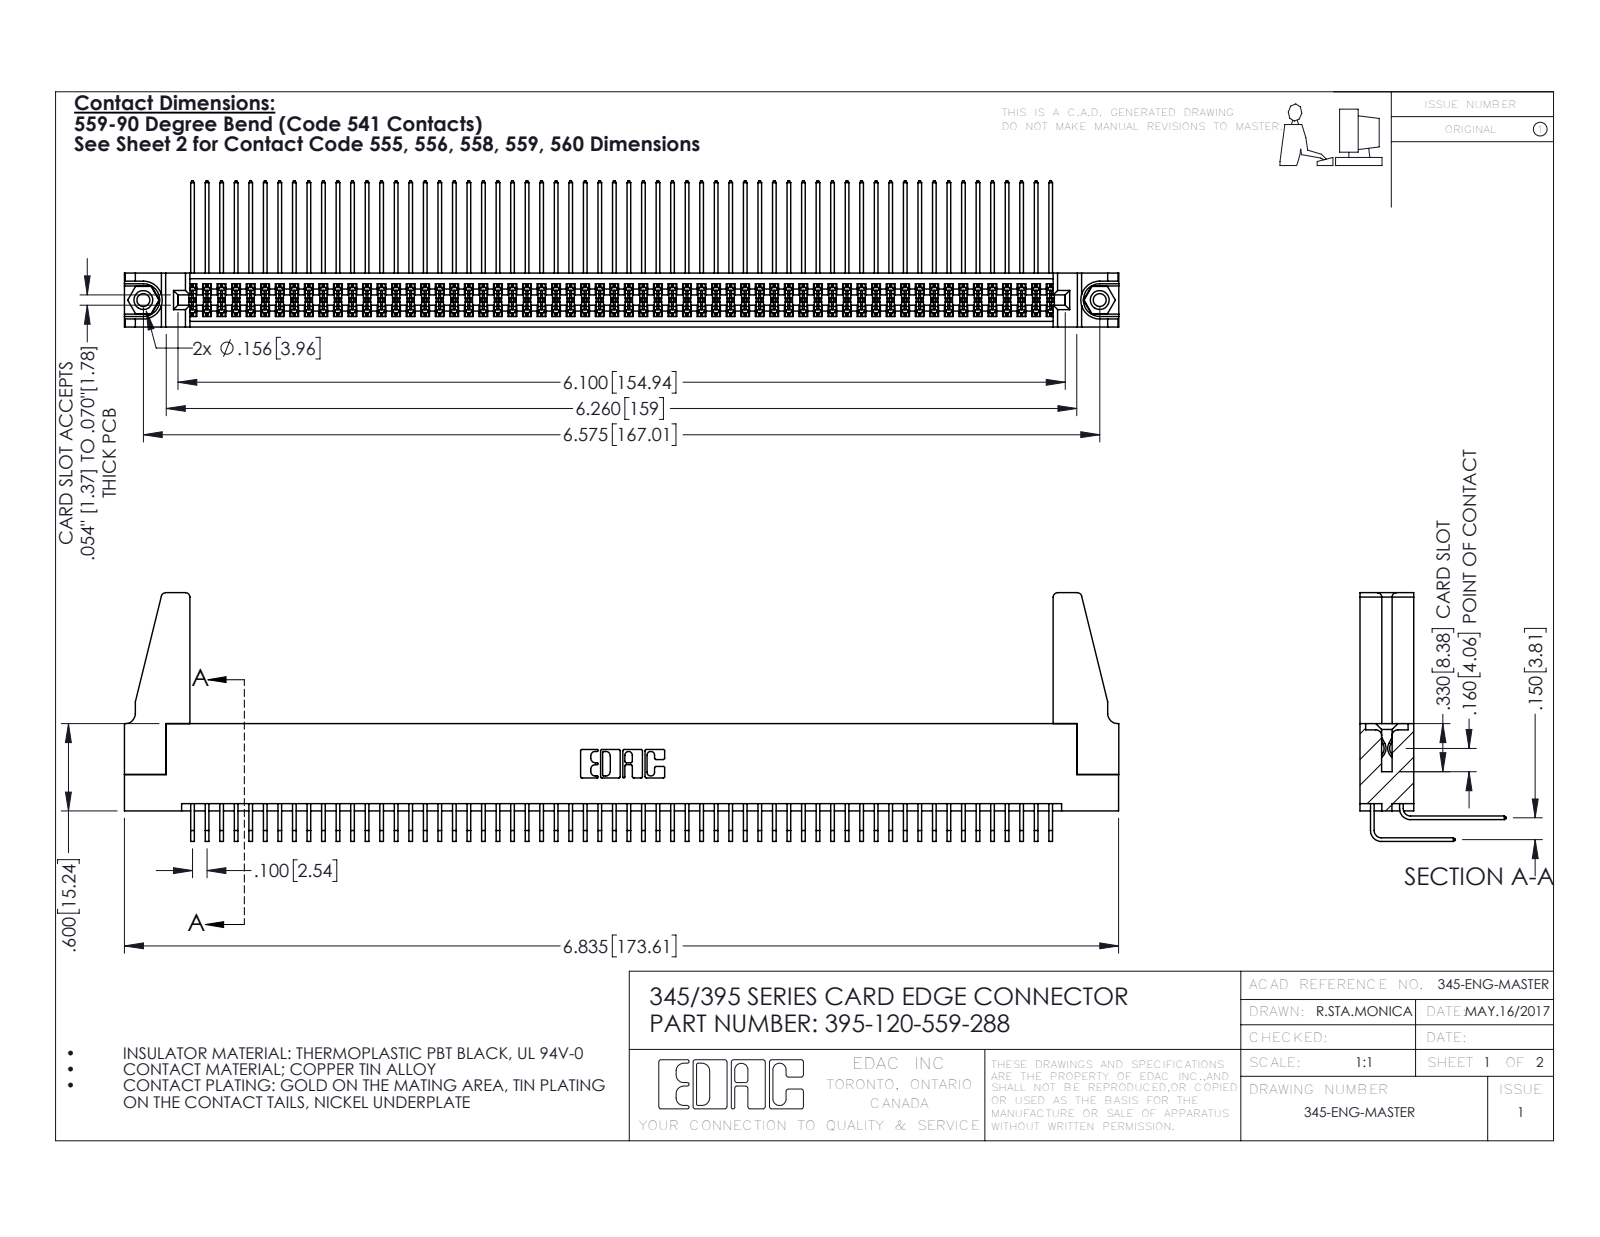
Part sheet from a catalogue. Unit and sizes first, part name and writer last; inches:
Units: inches
Overall size (bounding box): 6.836 × 1.709 × 1.005
Round holes (diameter × count): ⌀0.089 ×2, ⌀0.125 ×2, ⌀0.156 ×2, ⌀0.064 ×1
Round bosses / shafts (diameter × count): ⌀0.155 ×2
Partial cylindrical surfaces — rounded edges, fillets, slot ends (radius × count): R0.006 ×181, R0.01 ×22, R0.03 ×8, R0.007 ×6, R0.031 ×6, R0.026 ×3, R0.014 ×2, R0.019 ×2
Main face-to-face distances: 0.072, 0.298, 0.37, 0.2, 0.098, 0.272, 0.025, 0.225, 0.175, 0.15
Hole centre spacings: 0.27, 6.339, 6.575
Volume: 1.28 in³ · Surface area: 51.04 in²
Bodies: 125 solids, 6490 faces (4352 planar, 2122 cylindrical, 16 other)
Part name (STEP PRODUCT): 345 Part_Flush Mounting Lugs - 0.156 Dia-TH; 345-250-001_345-250-001-102; 345-292-001_559 Tail - 2; 345-292-001_558 559 Tail - 1 (+2 more)
STEP written by: SolidWorks 2016 (CONFIG_CONTROL_DESIGN)
